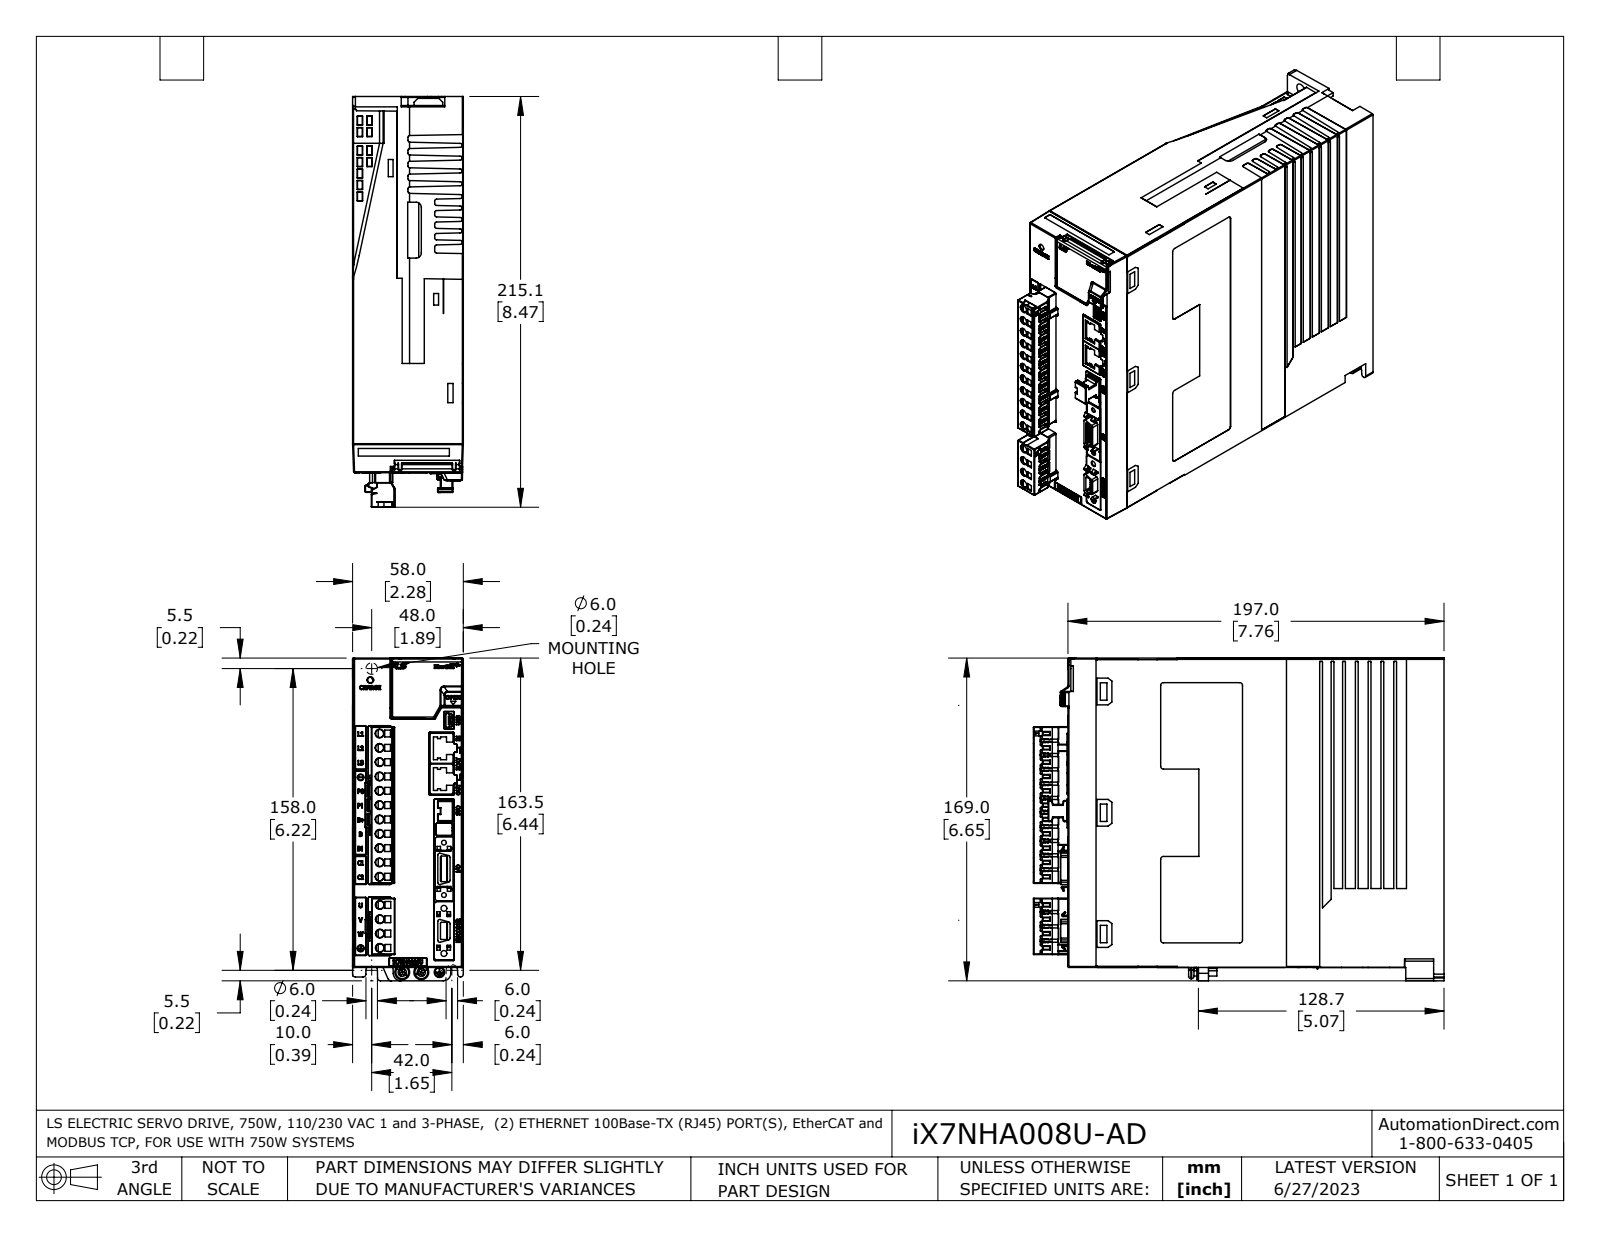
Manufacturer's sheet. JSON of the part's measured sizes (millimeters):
{"part_name": "OUTLINE (iX7NHA008U, iX7NHA010U) 46 faces broken 1 ext1ac -tbs fcons wash aa2 B1bcec NTBs", "step_written_by": "SolidWorks 2021 (AUTOMOTIVE_DESIGN)", "units": "millimeters", "bodies": {"solids": 12, "faces": 5296, "planar": 3519, "cylindrical": 812, "other": 965}, "overall_size": [215.1, 169.1, 58], "volume_mm3": 1876000, "surface_area_mm2": 164600, "round_holes": [[4.2, 15], [2.5, 2], [3.1, 2], [3.2, 2], [1.7, 1], [2.9, 1], [5.5, 1], [6, 1]], "round_bosses_or_shafts": [[5.3, 3], [3, 3], [4, 2], [7.8, 1], [6.7, 1], [4.7, 1], [3.7, 1], [3.5, 1]], "partial_cylinders_radius": [[0.3, 162], [0.5, 116], [0.2, 95], [0.4, 71], [1, 36], [0.9, 12], [0.4, 11], [0.5, 10]], "face_to_face_distances": [58, 58, 162, 14.7, 182.3, 197, 5.4, 176.9, 191.6, 162], "hole_center_spacings": [7.5, 15, 22.5, 30, 37.5, 45, 37.3, 44.8]}
